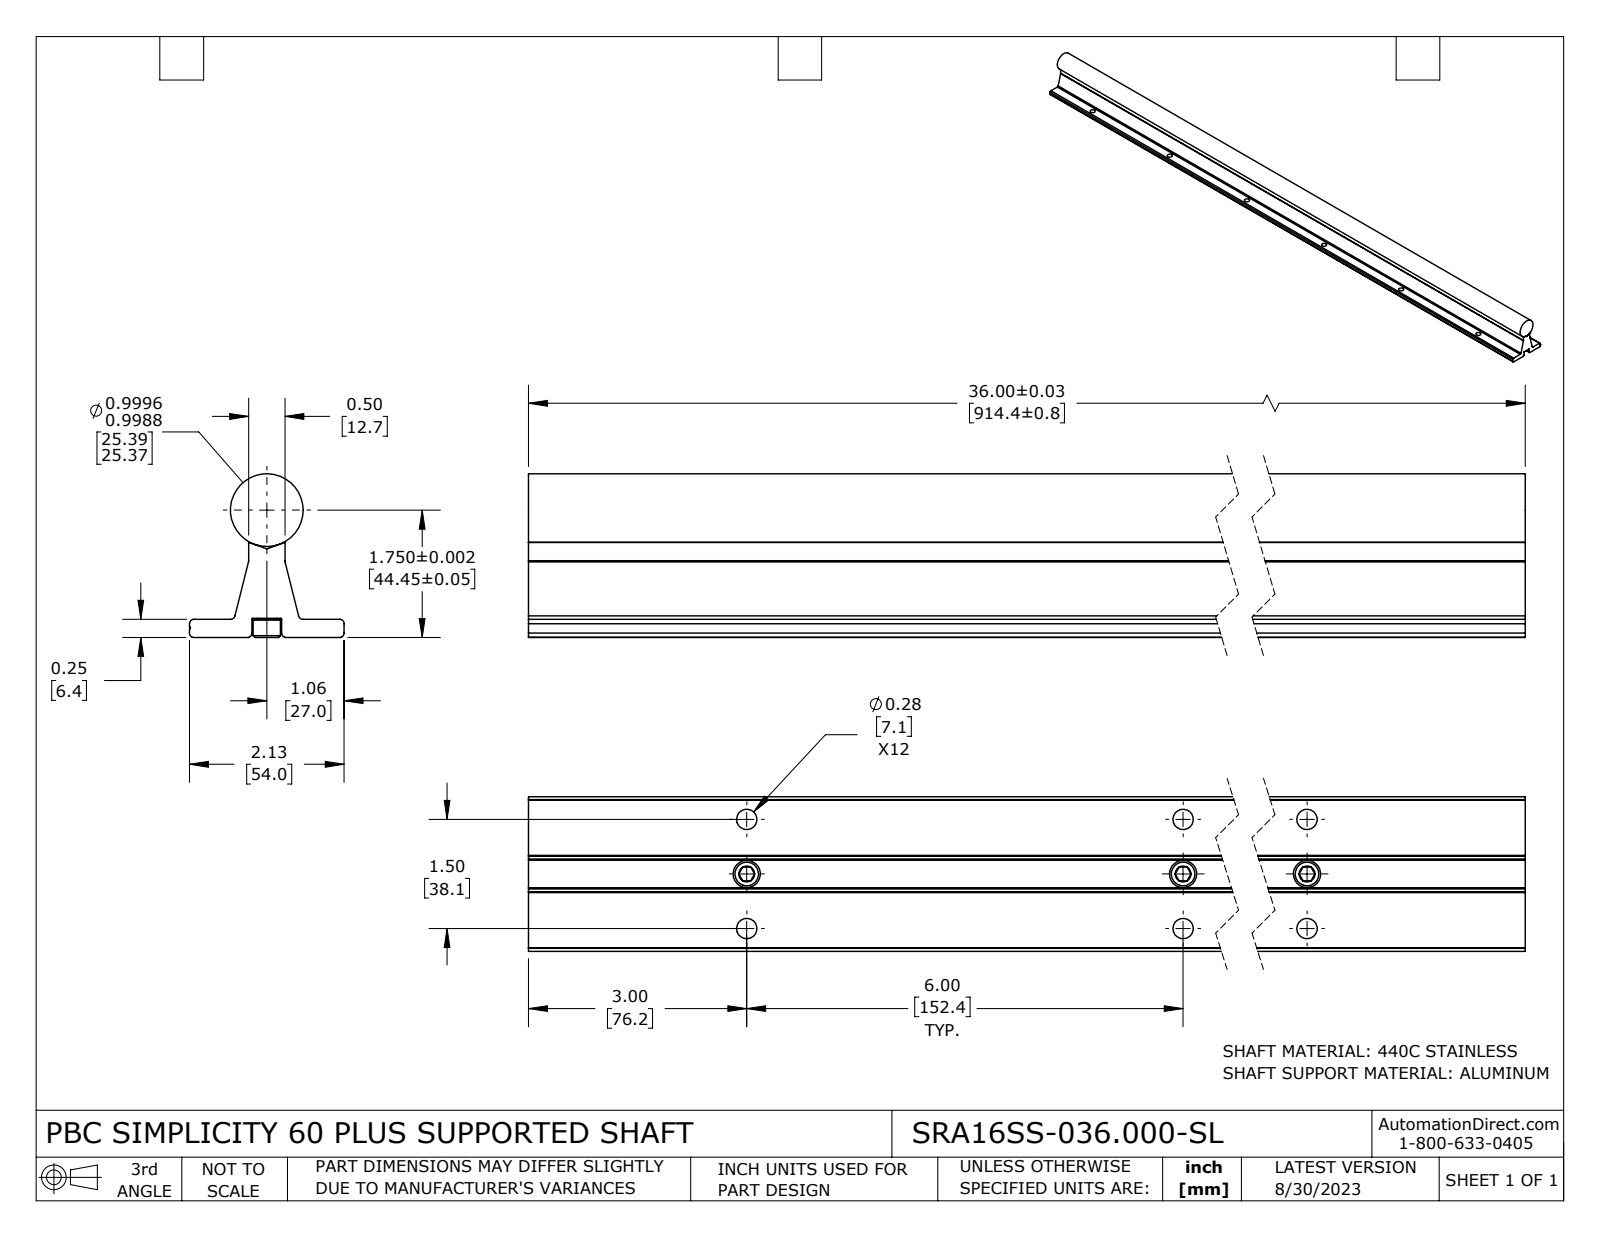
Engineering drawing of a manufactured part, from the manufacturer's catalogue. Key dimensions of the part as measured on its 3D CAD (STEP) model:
Part name (STEP PRODUCT): SRA16SS-036.000-SL
STEP written by: SolidWorks 2021 (CONFIG_CONTROL_DESIGN)
Units: inches
Bodies: 8 solids, 283 faces (93 planar, 100 cylindrical, 90 other)
Overall size (bounding box): 36 × 2.25 × 2.125
Volume: 67.13 in³ · Surface area: 384.3 in²
Round holes (diameter × count): ⌀0.281 ×18, ⌀0.213 ×6, ⌀0.313 ×6
Round bosses / shafts (diameter × count): ⌀0.375 ×6, ⌀0.25 ×6, ⌀1 ×1
Partial cylindrical surfaces — rounded edges, fillets, slot ends (radius × count): R0.06 ×6, R0.063 ×4, R0.015 ×2, R0.032 ×2
Main face-to-face distances: 0.25, 0.045, 0.455, 0.265, 0.015, 0.5, 0.813, 0.857, 1.268, 1.313
Hole centre spacings: 6.047, 12.023, 6, 0.75, 12, 18.016, 6.185, 18
